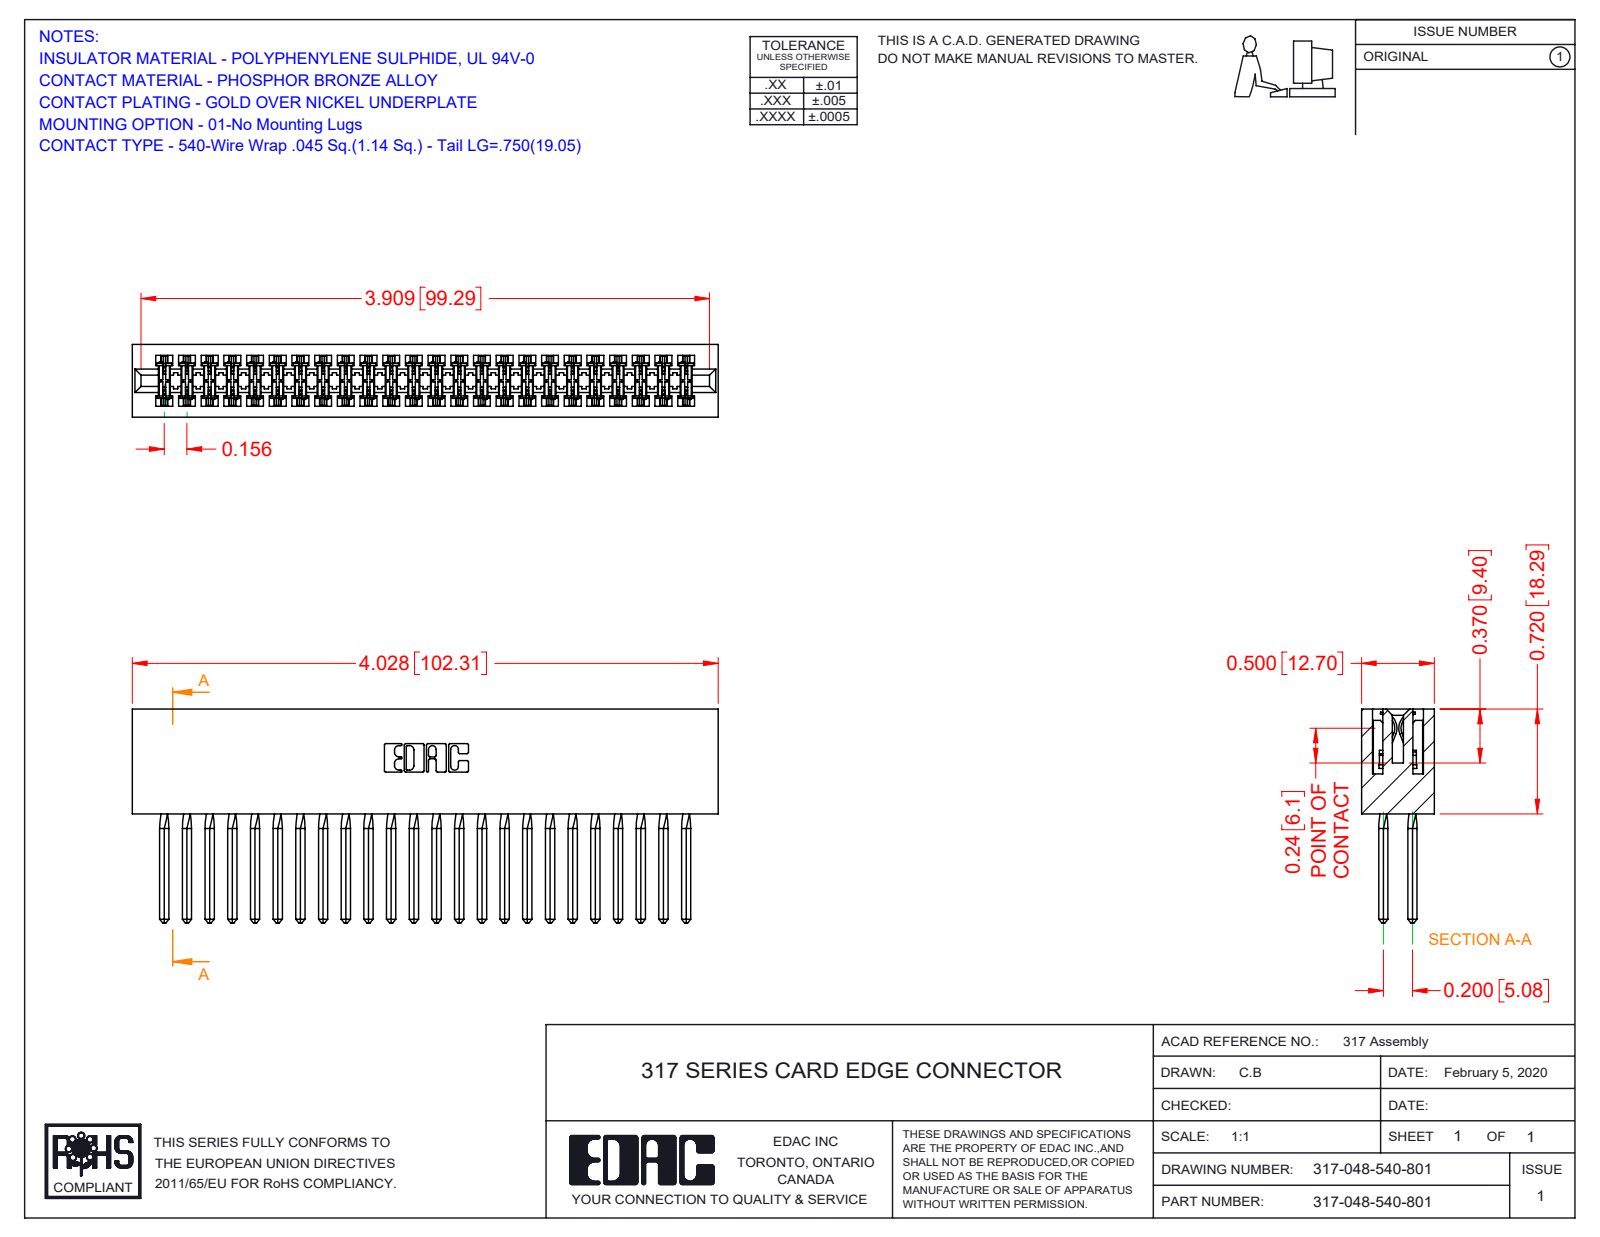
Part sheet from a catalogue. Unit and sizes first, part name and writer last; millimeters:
Units: millimetres
Overall size (bounding box): 102.3 × 37.3 × 12.7
Partial cylindrical surfaces — rounded edges, fillets, slot ends (radius × count): R0.4 ×96, R0.3 ×22, R0.2 ×6, R0.8 ×6, R0.7 ×3, R2.4 ×2, R2.5 ×2, R2.8 ×2
Main face-to-face distances: 1.9, 12.7, 10.8, 8.9, 2.8, 5, 2.9, 2.4, 18.3, 5.1
Volume: 18 350 mm³ · Surface area: 26 940 mm²
Bodies: 49 solids, 4362 faces (3554 planar, 616 cylindrical, 192 other)
Part name (STEP PRODUCT): 317 Part_Lugless; 317-048-540-801; 317-290-001_540
STEP written by: SolidWorks 2016 (CONFIG_CONTROL_DESIGN)
